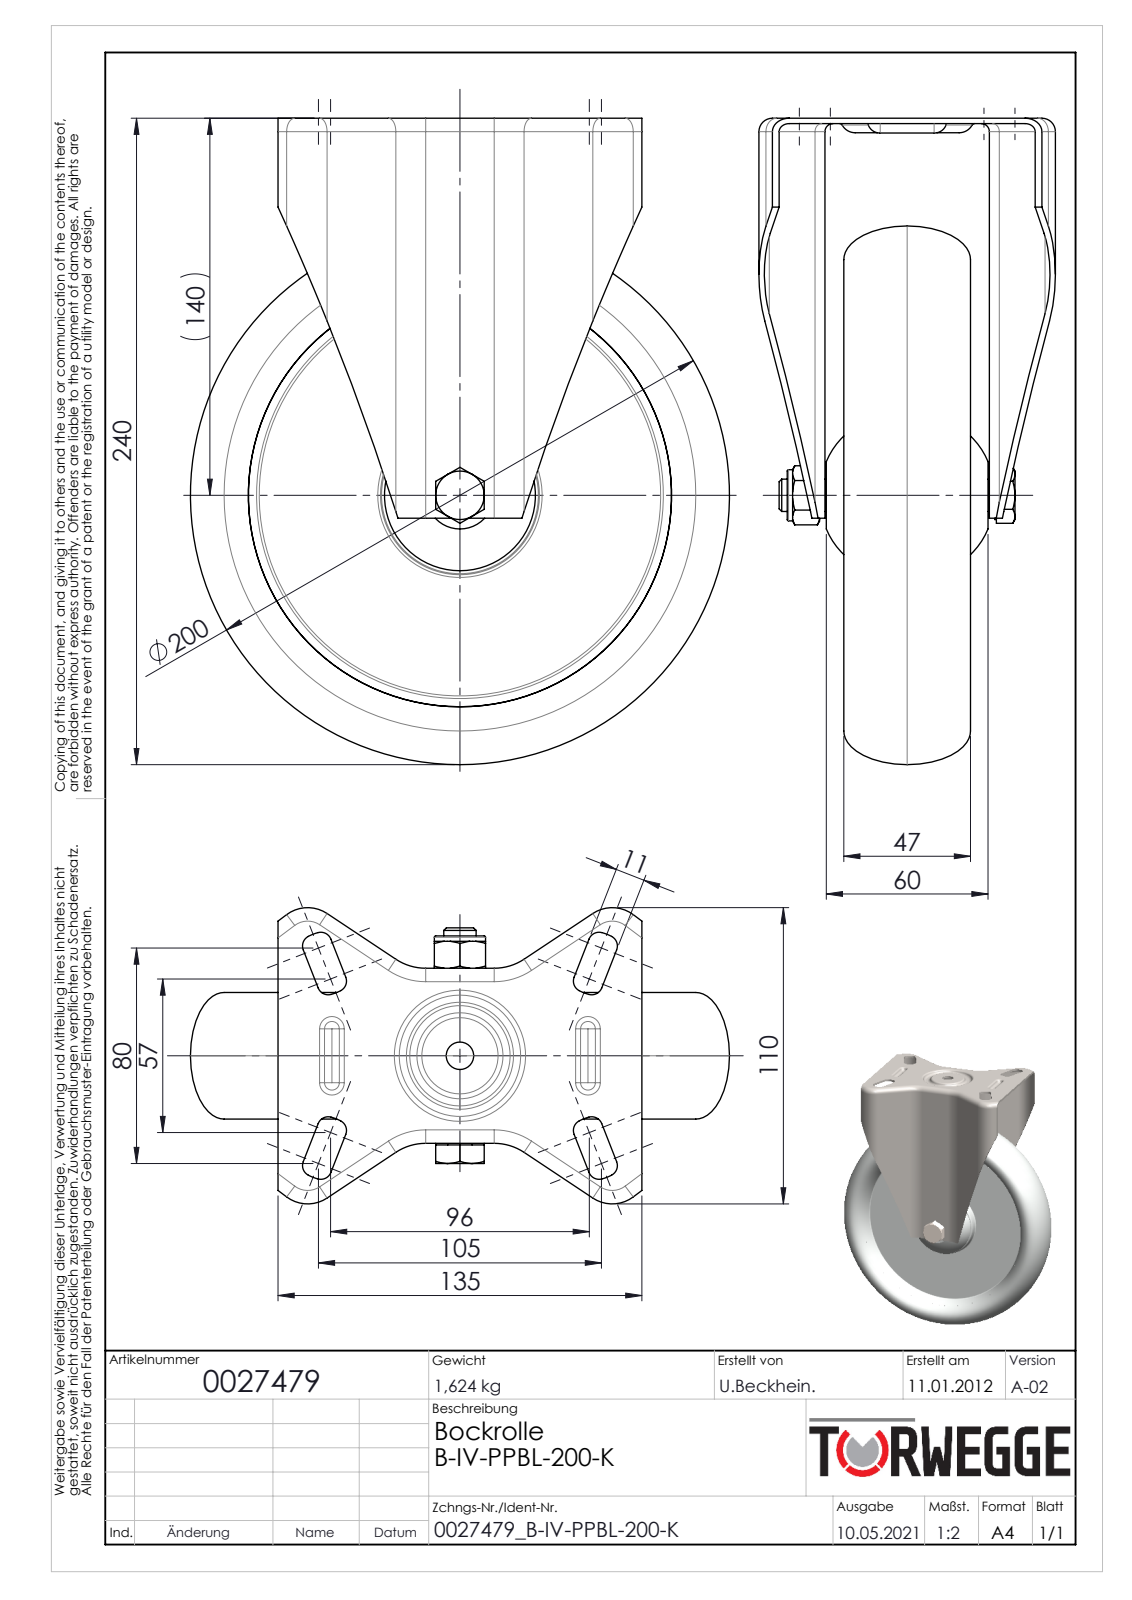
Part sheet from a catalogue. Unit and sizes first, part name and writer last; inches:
Units: inches
Overall size (bounding box): 9.449 × 7.874 × 4.331
Round holes (diameter × count): ⌀0.402 ×2, ⌀0.472 ×1, ⌀0.492 ×1, ⌀1.106 ×1, ⌀1.531 ×1, ⌀1.732 ×1, ⌀1.85 ×1
Round bosses / shafts (diameter × count): ⌀1.614 ×1, ⌀0.787 ×1, ⌀0.748 ×1, ⌀0.709 ×1
Partial cylindrical surfaces — rounded edges, fillets, slot ends (radius × count): R0.157 ×16, R0.118 ×12, R0.197 ×10, R0.703 ×8, R0.079 ×4, R0.181 ×4, R0.433 ×4, R0.512 ×4
Main face-to-face distances: 0.079, 0.433, 1.235, 1.063, 1.496, 2.48, 0.984, 1.417, 1.314, 1.157
Volume: 53.8 in³ · Surface area: 444.5 in²
Bodies: 12 solids, 397 faces (93 planar, 136 cylindrical, 168 other)
Part name (STEP PRODUCT): 0027479
STEP written by: SolidWorks 2020 (AUTOMOTIVE_DESIGN)
